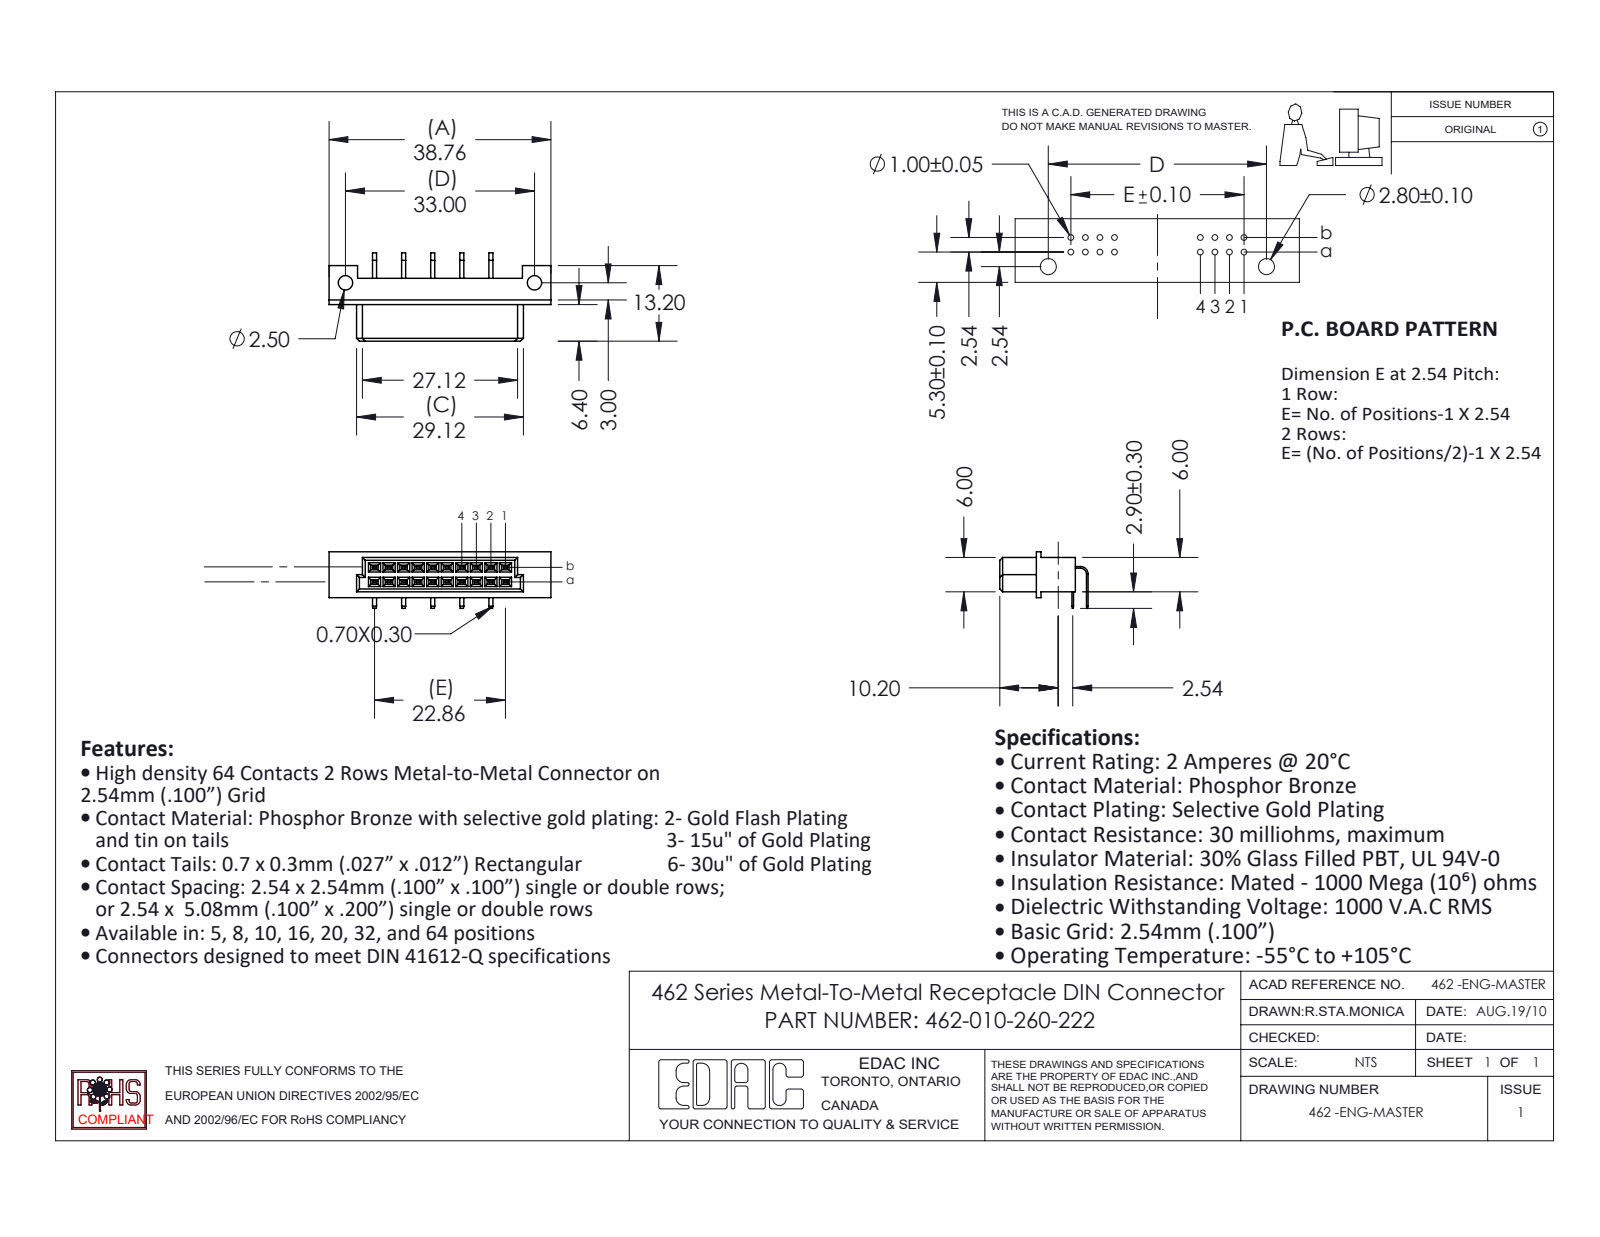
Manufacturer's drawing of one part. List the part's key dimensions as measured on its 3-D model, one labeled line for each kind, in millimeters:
Part name (STEP PRODUCT): 462-290-2; 462 Part_20; 462-010-260-222; 462-290-1
STEP written by: SolidWorks 2020 (CONFIG_CONTROL_DESIGN)
Units: millimetres
Bodies: 11 solids, 435 faces (411 planar, 24 cylindrical, 0 other)
Overall size (bounding box): 38.76 × 15.43 × 9.9
Volume: 2 136 mm³ · Surface area: 2 571 mm²
Round holes (diameter × count): ⌀2.5 ×2
Partial cylindrical surfaces — rounded edges, fillets, slot ends (radius × count): R1.02 ×2, R1.32 ×2
Main face-to-face distances: 6, 2.54, 4.6, 0.81, 1.58, 1.88, 4.12, 4.42, 0.56, 0.55
Hole centre spacings: 33
